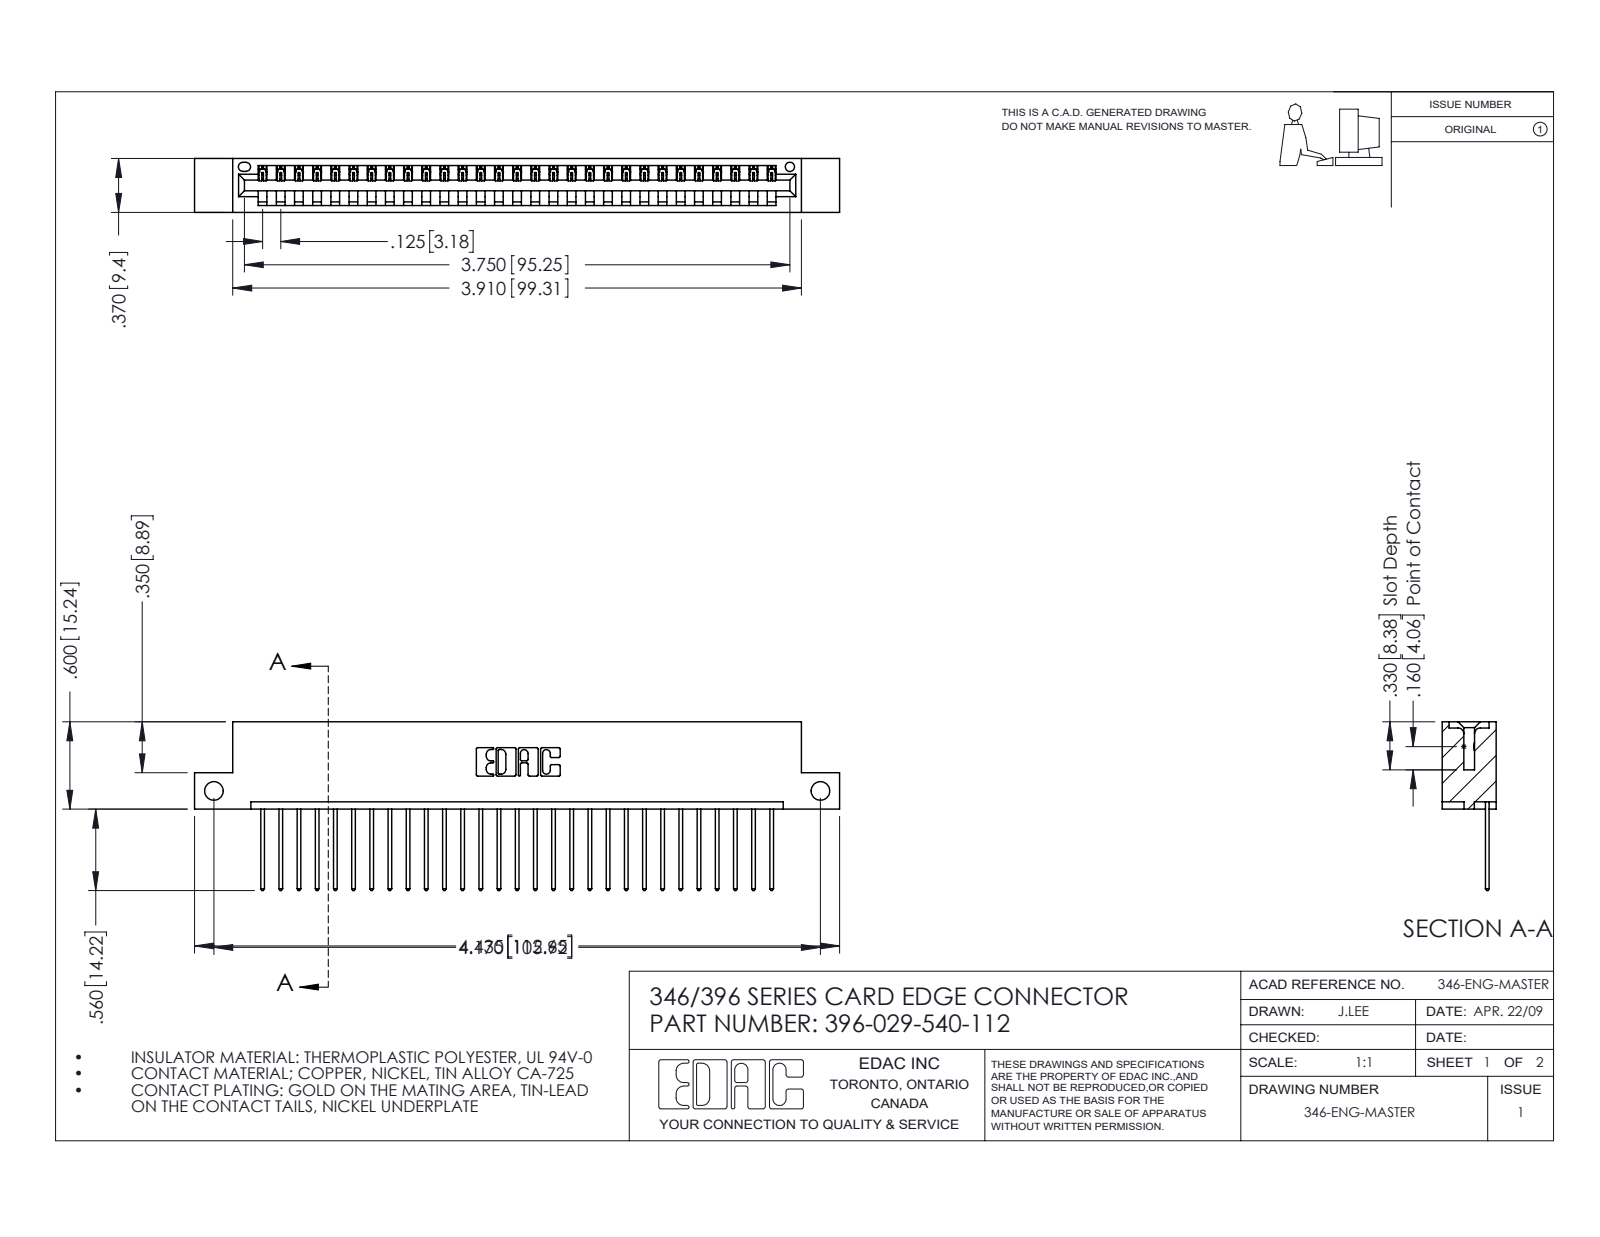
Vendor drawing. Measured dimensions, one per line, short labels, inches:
name: 345-292-001_345-293-140; 346 Part_Flush Mounting Lugs - Side Mount; 396-029-540-112
written by: SolidWorks 2016 (CONFIG_CONTROL_DESIGN)
unit: in
bodies: 30 solids, 1804 faces (1236 planar, 568 cylindrical, 0 other)
size: 4.435 × 1.16 × 0.37
volume: 0.65 in³; area: 20.62 in²
holes: 2× ⌀0.128, 1× ⌀0.064
rounds: 58× R0.006, 58× R0.01, 22× R0.01, 6× R0.007, 6× R0.031, 3× R0.026, 2× R0.031, 2× R0.04
face distances: 0.048, 0.322, 0.25, 0.37, 0.072, 0.298, 0.025, 0.148, 0.222, 0.1
hole spacings: 4.17
